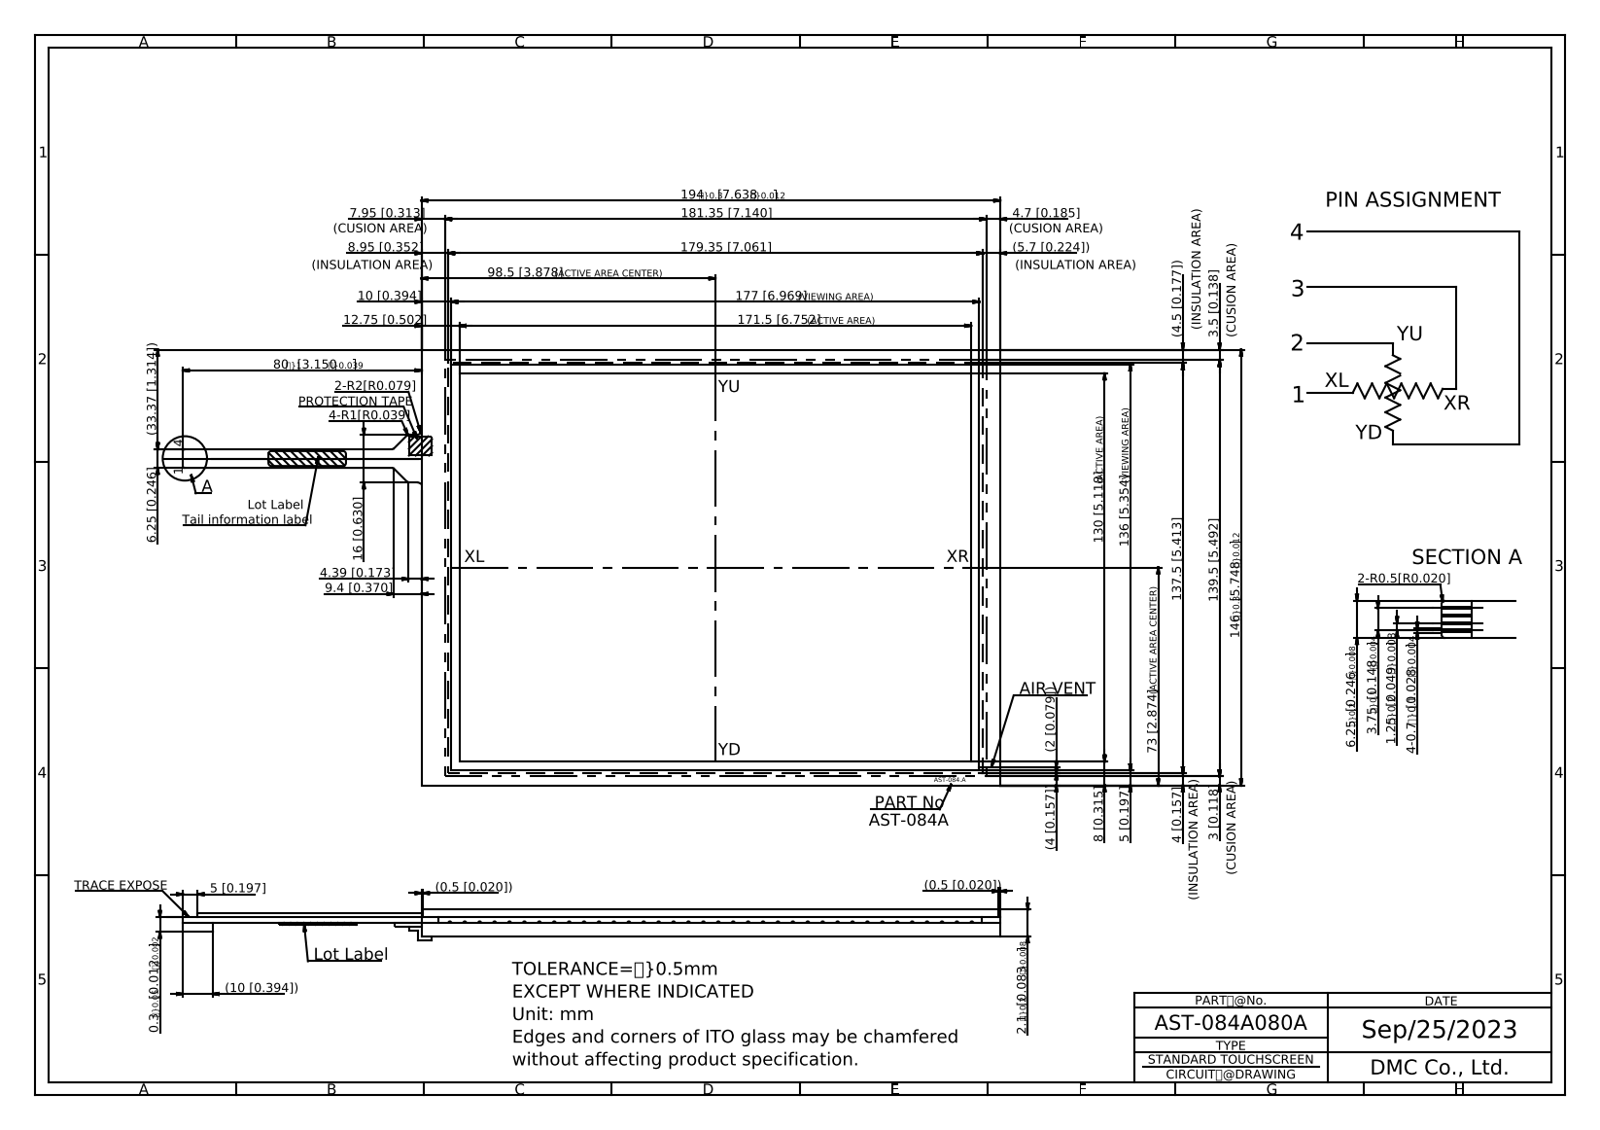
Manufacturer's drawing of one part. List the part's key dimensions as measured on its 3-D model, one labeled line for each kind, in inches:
Part name (STEP PRODUCT): AST-084A080A
STEP written by: Autodesk Inventor 2020 (CONFIG_CONTROL_DESIGN)
Units: inches
Bodies: 1 solid, 51 faces (45 planar, 6 cylindrical, 0 other)
Overall size (bounding box): 12.315 × 8.047 × 0.083
Volume: 3.623 in³ · Surface area: 92 in²
Partial cylindrical surfaces — rounded edges, fillets, slot ends (radius × count): R0.039 ×4, R0.02 ×2
Main face-to-face distances: 0.083, 0.079, 0.075, 0.071, 5.748, 7.638, 0.059, 0.016, 0.02, 0.024
